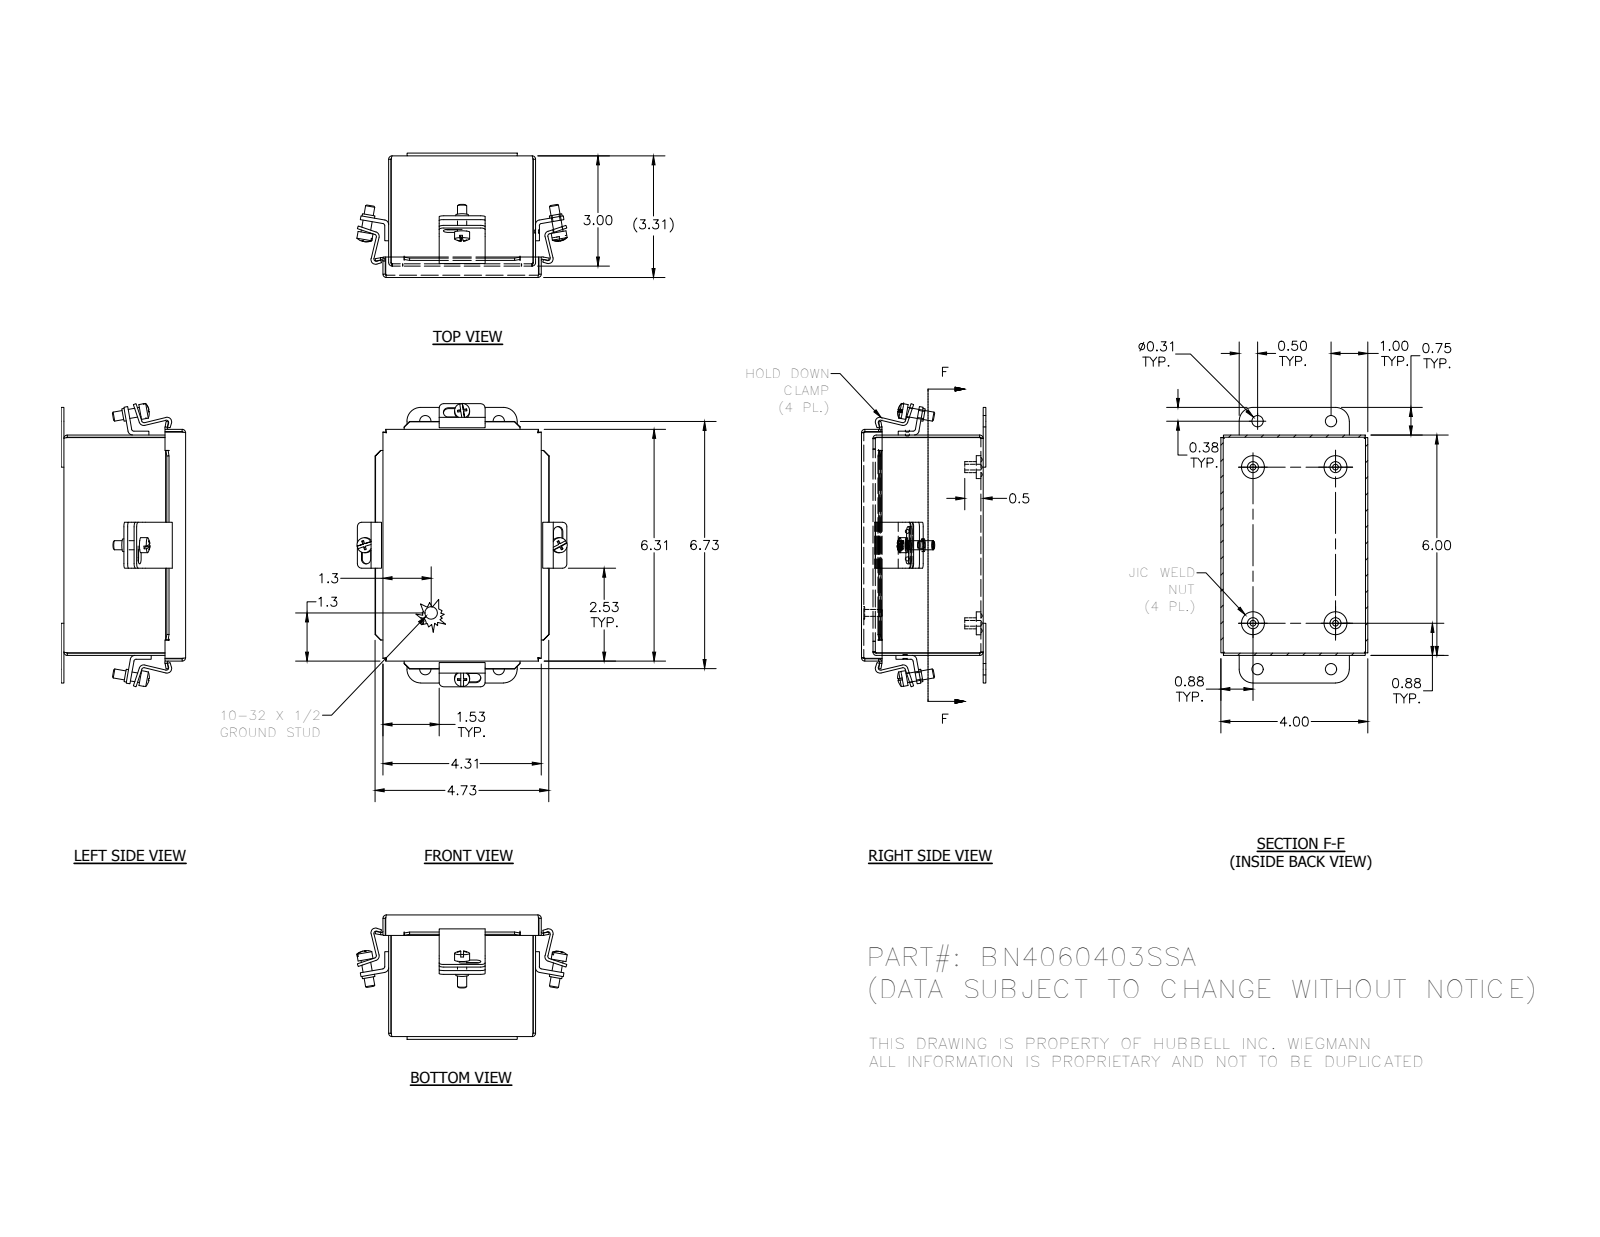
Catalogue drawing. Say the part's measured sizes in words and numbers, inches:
The part is named "BN4060403SSABKP_1; BN40604SSALID_1; 30811_1; HFW3883 (+5 more)". Its 3-D file was written by "SolidWorks 2014 (AUTOMOTIVE_DESIGN)". It is 21 solids with 589 faces: 287 planar, 200 cylindrical and 102 other. Overall it measures 7.713 by 5.724 by 3.388 inches. Its volume is 10.2 cubic inches and its surface area 317.4 square inches. Round holes: 6 of diameter 0.11, 4 of diameter 0.156, 4 of diameter 0.196, 4 of diameter 0.31. Round bosses or shafts: 4 of diameter 0.625, 4 of diameter 0.41, 4 of diameter 0.344, 4 of diameter 0.3, 4 of diameter 0.25, 1 of diameter 0.337, 1 of diameter 0.19. Partial cylindrical surfaces (rounded edges, fillets, slot ends): 16 of radius 0.031, 16 of radius 0.094, 16 of radius 0.125, 12 of radius 0.063, 12 of radius 0.126, 8 of radius 0.133, 4 of radius 0.375. The main face-to-face distances are 0.063, 3.25, 3.937, 3.313, 3.187, 5.937, 4, 3.875, 0.075, 0.155. The hole center spacings are 1.256, 5.502, 0.75, 0.063, 0.753, 2, 2.25, 2.465.
